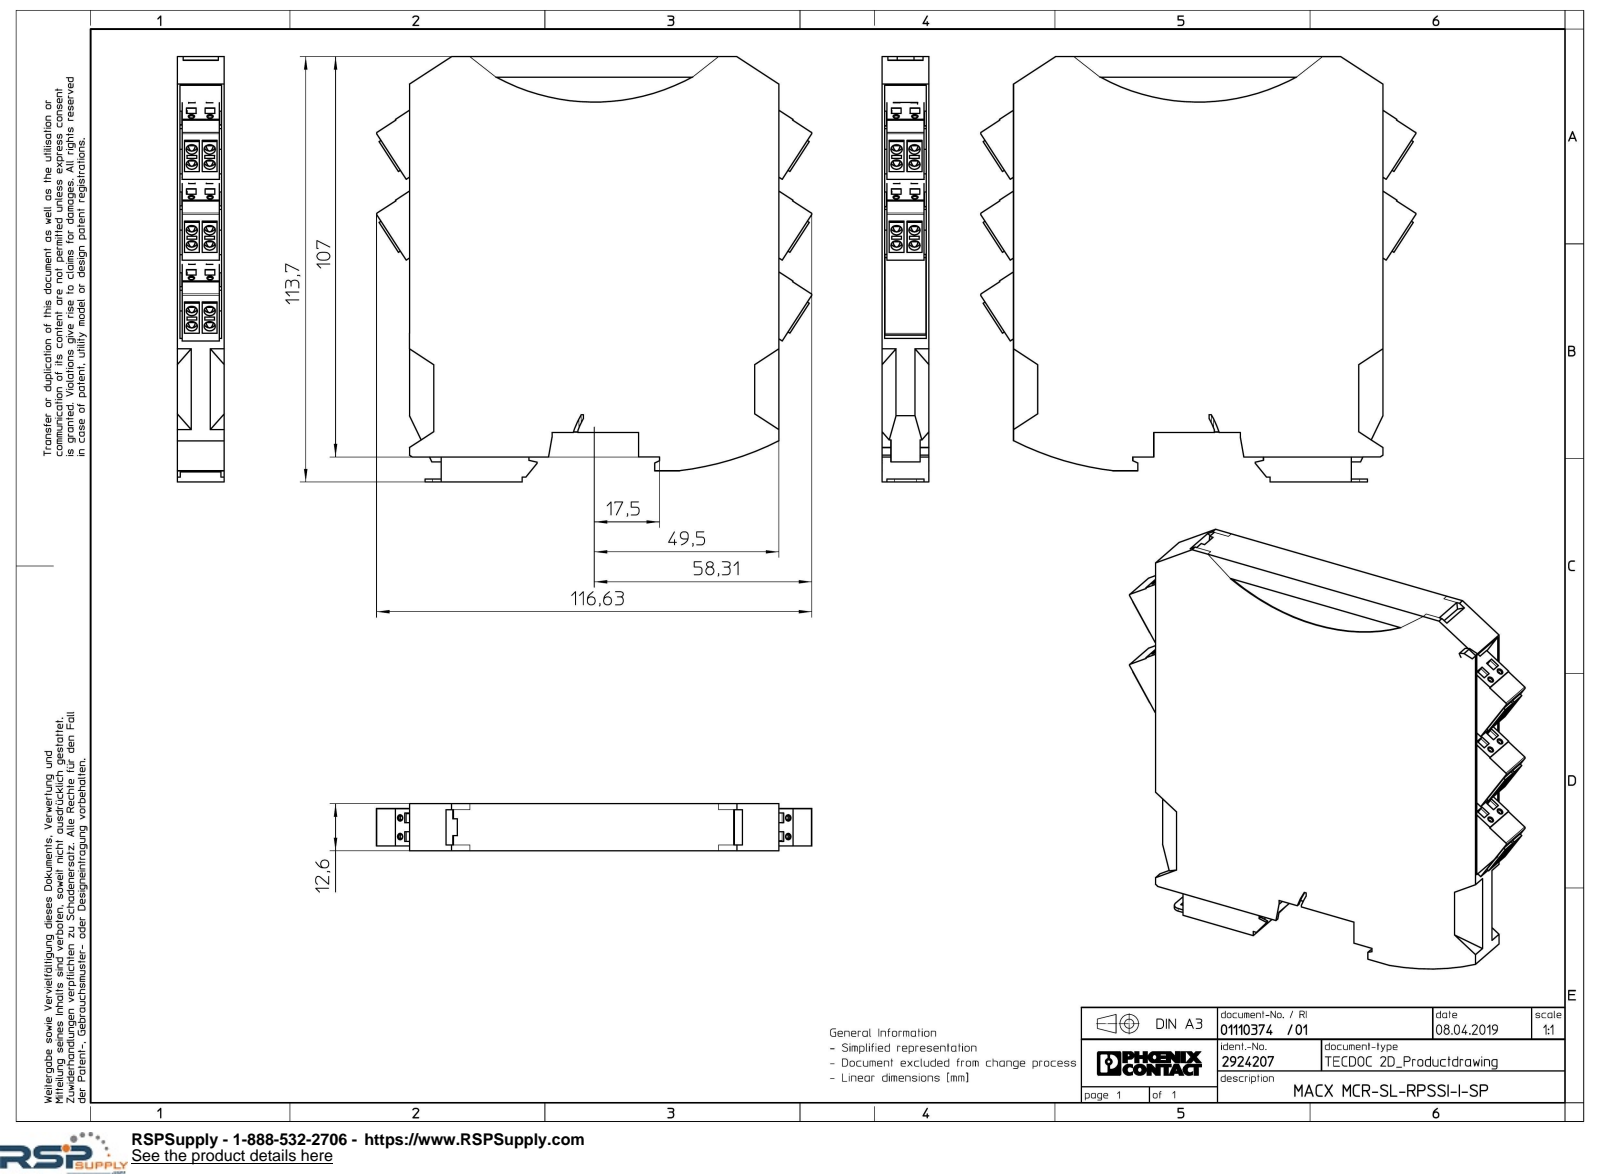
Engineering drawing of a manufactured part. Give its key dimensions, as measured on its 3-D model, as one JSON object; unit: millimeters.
{"part_name": "MAXC_12.5-GY-SOCKEL-select; ME_MAX_B-12.5_GY7042-select; TVFKC_1.5_2-ST_GY7035-select.2; MACX_MCR_12.5_152_1-select", "step_written_by": "Creo Elements/Direct Modeling 20.1A 29-Sep-2018 (C) Parametric Technology GmbH (AUTOMOTIVE_DESIGN)", "units": "millimeters", "bodies": {"solids": 7, "faces": 1208, "planar": 920, "cylindrical": 198, "other": 90}, "overall_size": [116.63, 113.7, 12.6], "volume_mm3": 129364, "surface_area_mm2": 43272, "round_holes": [[3, 30], [1.3, 10], [1.53, 10]], "round_bosses_or_shafts": [[2.8, 6]], "partial_cylinders_radius": [[1.25, 20], [3, 13], [2.9, 10], [1.4, 6], [0.3, 5], [2, 2], [0.5, 1], [1.5, 1]], "face_to_face_distances": [12.6, 11.3, 1.3, 0.75, 0.55, 10.55, 11.85, 18.12, 10, 11.1], "hole_center_spacings": [18.11, 4.8, 5, 5.05, 6.82, 1.23, 3.62, 4.85]}
